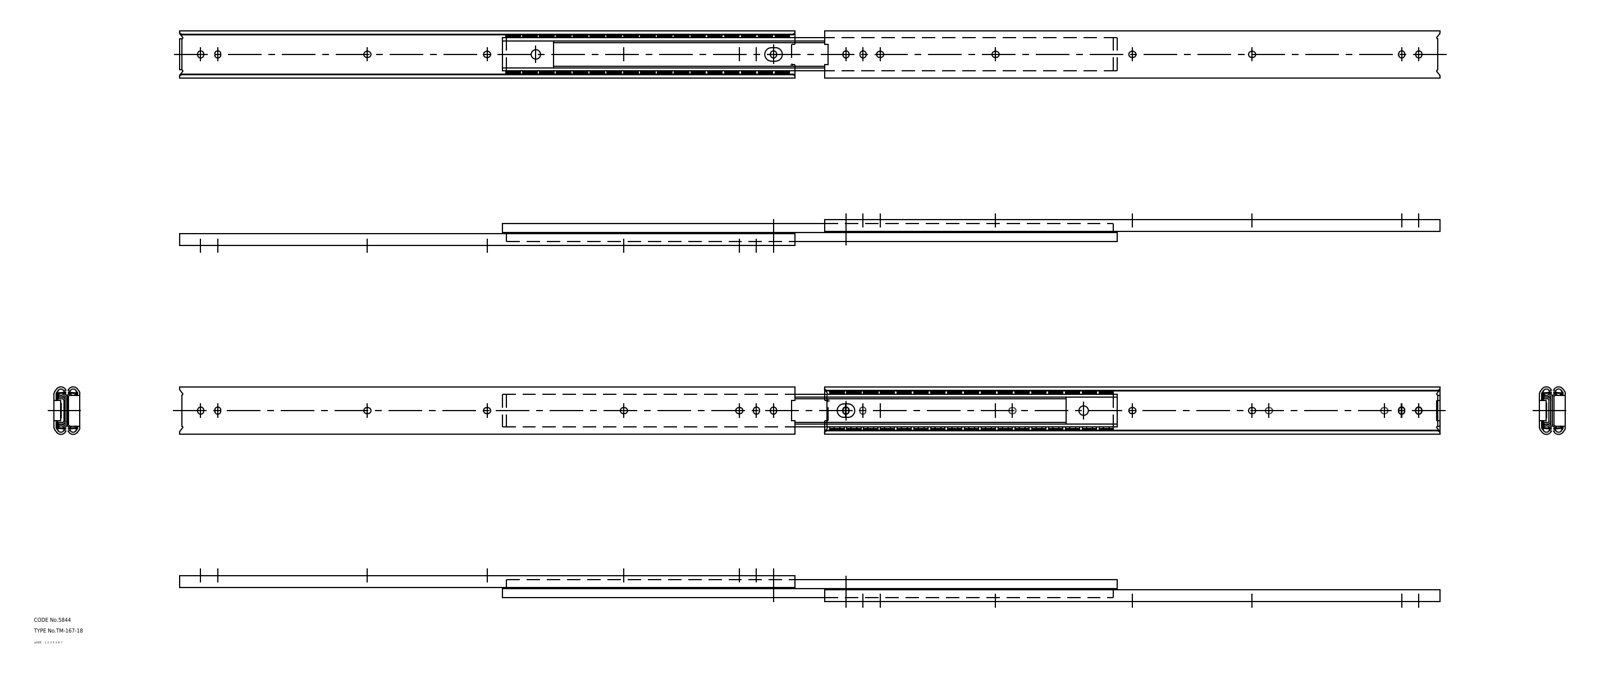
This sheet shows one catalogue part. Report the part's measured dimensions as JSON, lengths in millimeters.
{"part_name": "retainer_mr-1; ball; member_B_mr-1; member_A_mr-1 (+4 more)", "step_written_by": "CADfix (AUTOMOTIVE_DESIGN)", "units": "millimeters", "bodies": {"solids": 74, "faces": 988, "planar": 0, "cylindrical": 0, "other": 988}, "overall_size": [936, 35.3, 19.1], "volume_mm3": 138140, "surface_area_mm2": 200146}
